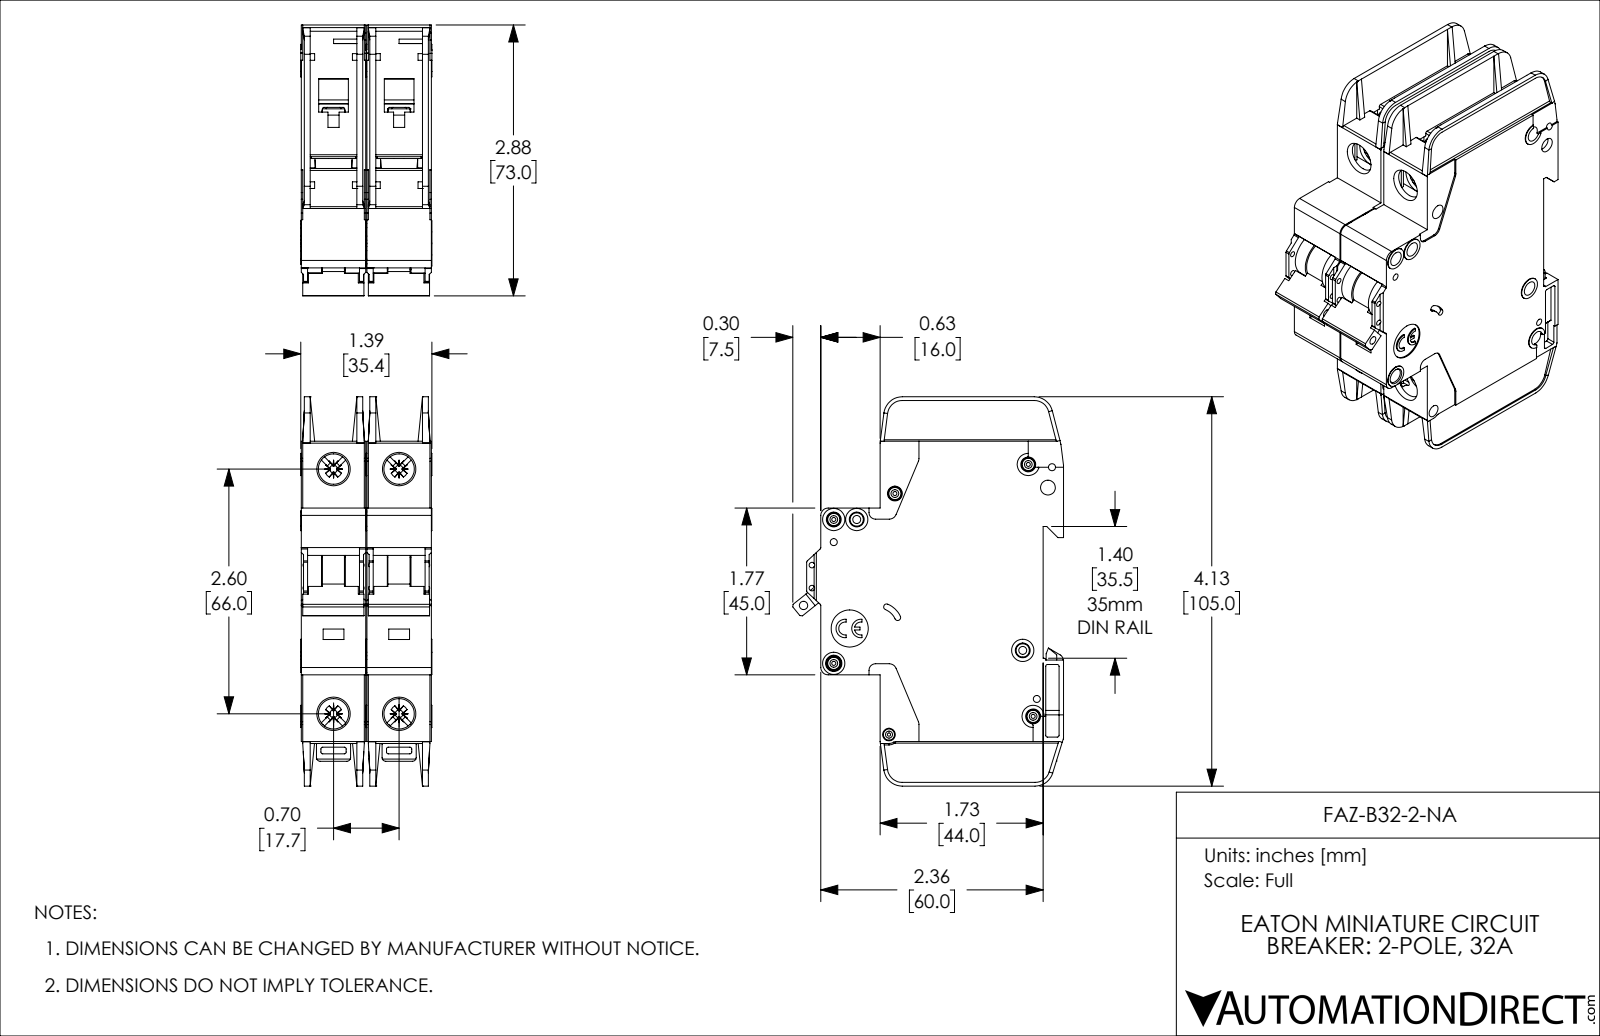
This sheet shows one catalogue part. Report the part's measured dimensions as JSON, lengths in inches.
{"part_name": "FAZ-B32-2-NA", "step_written_by": "SolidWorks 2019 (AUTOMOTIVE_DESIGN)", "units": "inches", "bodies": {"solids": 2, "faces": 2254, "planar": 1342, "cylindrical": 714, "other": 198}, "overall_size": [4.134, 2.876, 1.394], "volume_in3": 9.365, "surface_area_in2": 82.01, "round_holes": [[0.157, 8], [0.043, 5], [0.075, 4], [0.323, 4], [0.059, 2], [0.085, 2], [0.035, 1], [0.089, 1], [0.098, 1], [0.134, 1], [0.394, 1]], "round_bosses_or_shafts": [[0.13, 5], [0.236, 4], [0.118, 3], [0.098, 2]], "partial_cylinders_radius": [[0.02, 57], [0.016, 20], [0.039, 14], [0.079, 10], [0.043, 8], [0.008, 5], [0.197, 5], [0.01, 4]], "face_to_face_distances": [0.697, 0.047, 0.685, 0.591, 0.094, 0.638, 0.543, 1.382, 0.744, 0.65], "hole_center_spacings": [0.244, 0.537, 0.697, 0.87, 2.598, 2.69, 0.189, 0.199]}
